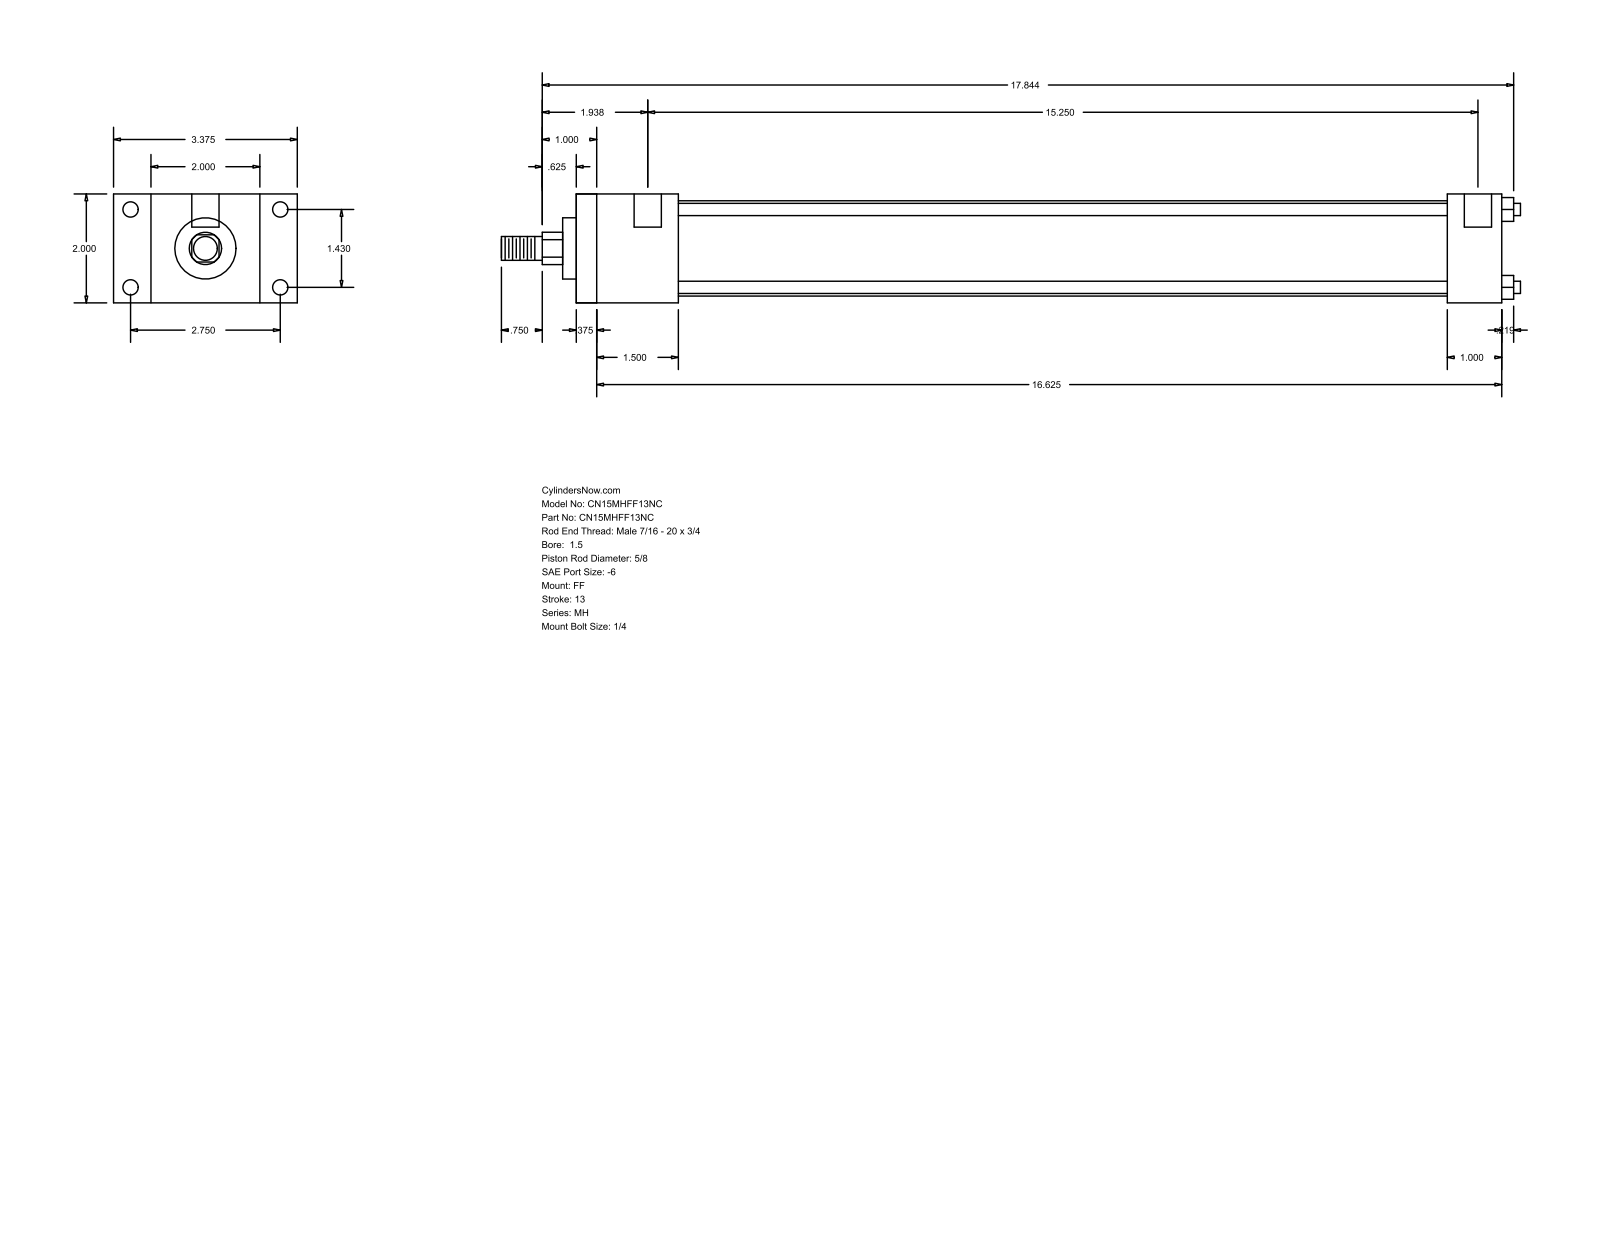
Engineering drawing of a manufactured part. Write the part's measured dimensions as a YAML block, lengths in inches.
part_name: "MH_FF__0150_0.625"
step_written_by: "GSSL Pune (CONFIG_CONTROL_DESIGN)"
units: inches
bodies: {solids: 0, faces: 92, planar: 64, cylindrical: 28, other: 0}
overall_size: [18.719, 3.375, 2]
round_holes:
  - {diameter: 0.219, count: 4}
  - {diameter: 0.281, count: 4}
  - {diameter: 0.5, count: 2}
round_bosses_or_shafts:
  - {diameter: 0.225, count: 4}
  - {diameter: 1.75, count: 1}
  - {diameter: 1.125, count: 1}
  - {diameter: 0.625, count: 1}
  - {diameter: 0.437, count: 1}
partial_cylinders:
  - {radius: 0.297, count: 1}
face_to_face_distances: [2, 17, 0.375, 16.625, 0.687, 2.687, 1.875, 1.5, 15.125, 16]
hole_center_spacings: [1.43, 2.75, 3.099, 15.375, 0.125, 15.25]
